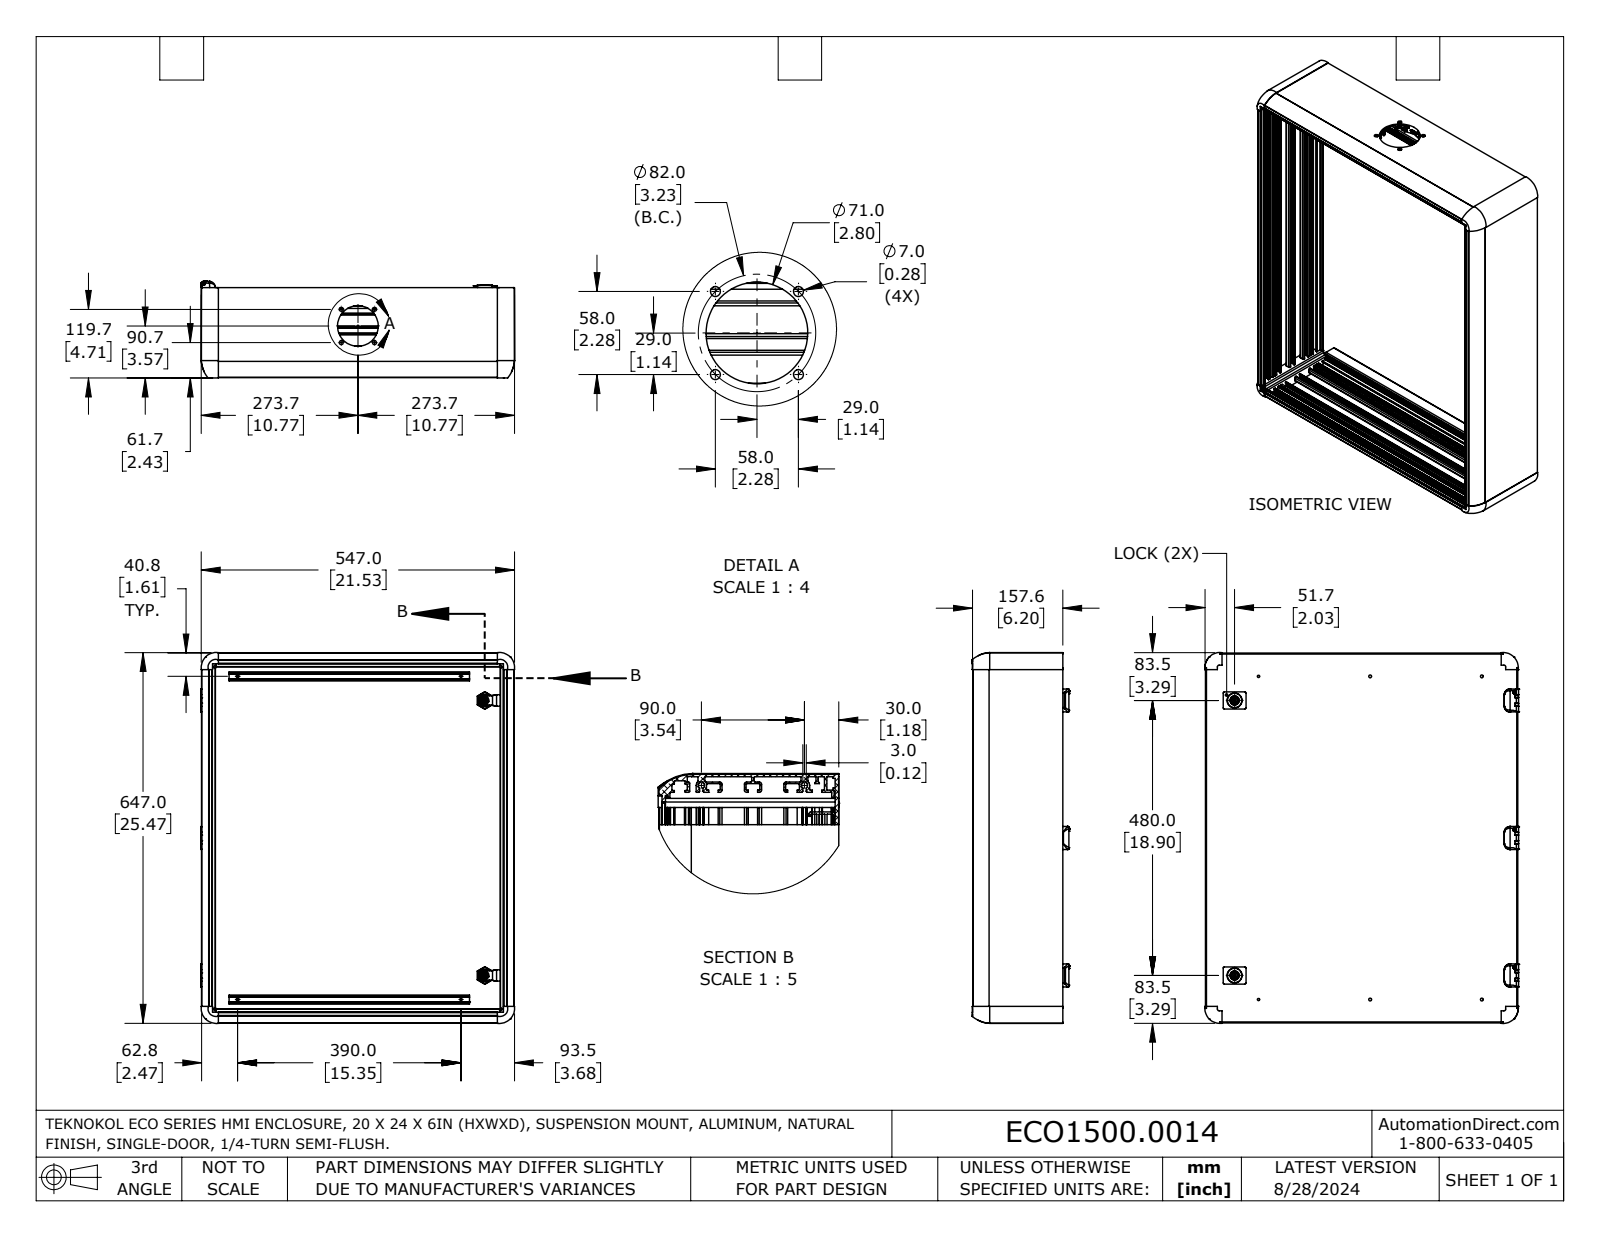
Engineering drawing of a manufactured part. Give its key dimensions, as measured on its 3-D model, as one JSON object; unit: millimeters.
{"part_name": "ECO.1500.0014(500x600)_REV3", "step_written_by": "SolidWorks 2023 (AUTOMOTIVE_DESIGN)", "units": "millimeters", "bodies": {"solids": 14, "faces": 3059, "planar": 1410, "cylindrical": 1034, "other": 615}, "overall_size": [647.5, 547.9, 168.7], "volume_mm3": 3482000, "surface_area_mm2": 2437000, "round_holes": [[4.3, 7], [5, 4], [7, 4], [4.4, 3], [4, 2], [5.2, 2], [15.3, 2], [16, 2], [10, 1], [71, 1]], "round_bosses_or_shafts": [[9.4, 3], [5.1, 3], [4.8, 3], [26, 2], [25.2, 2], [22.5, 2], [18, 2], [13.5, 2]], "partial_cylinders_radius": [[0.5, 275], [0.2, 98], [2, 65], [1, 58], [0.4, 28], [0.3, 24], [2.5, 18], [0.2, 12]], "face_to_face_distances": [3, 2.3, 543.3, 2, 643.3, 9, 13.5, 6, 8.3, 1.5], "hole_center_spacings": [240, 41, 58, 195, 480, 485.2, 596.7, 3.4]}
